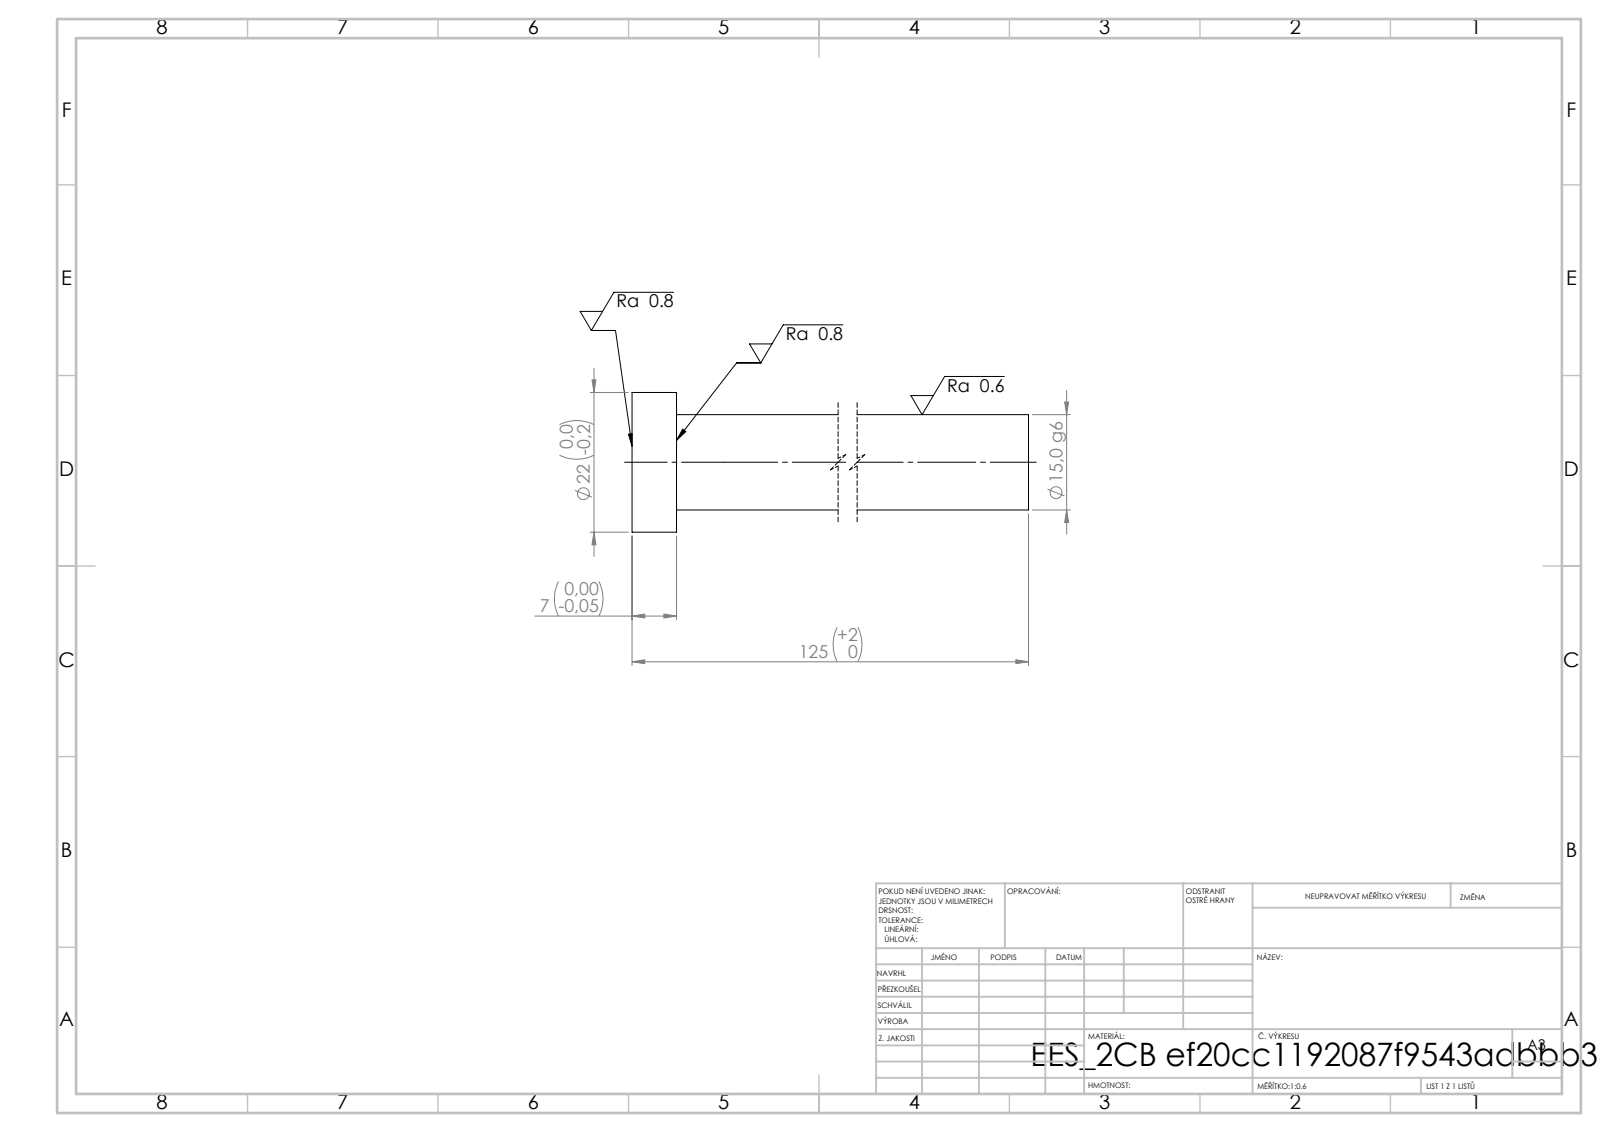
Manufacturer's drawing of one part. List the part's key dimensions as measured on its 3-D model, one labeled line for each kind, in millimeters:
STEP written by: SolidWorks 2019 (CONFIG_CONTROL_DESIGN)
Units: millimetres
Bodies: 1 solid, 7 faces (3 planar, 4 cylindrical, 0 other)
Overall size (bounding box): 125 × 22 × 22
Volume: 23 513 mm³ · Surface area: 6 805 mm²
Round bosses / shafts (diameter × count): ⌀22 ×1, ⌀15 ×1
Main face-to-face distances: 7, 125, 118
